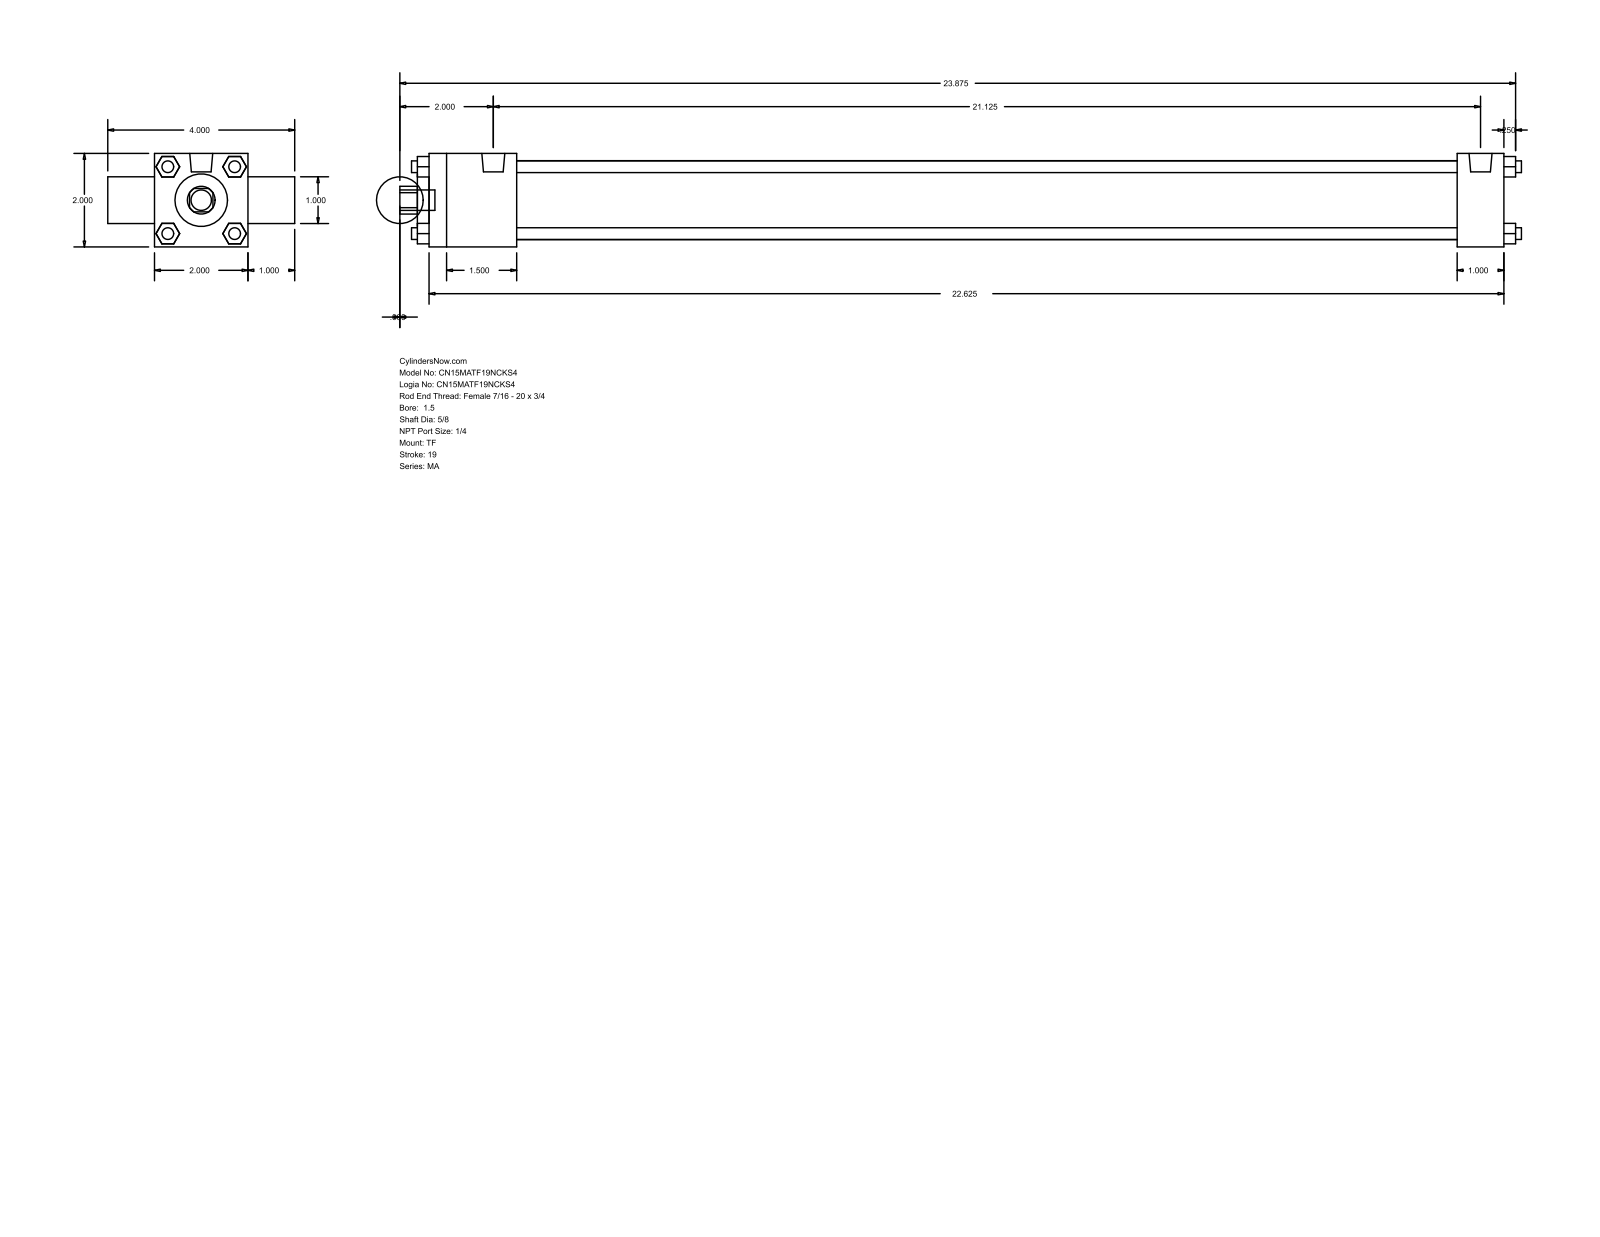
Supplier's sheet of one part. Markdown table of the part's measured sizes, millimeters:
| quantity | value |
| --- | --- |
| part name | MA_TF__0150_0.625 |
| STEP written by | GSSL Pune (CONFIG_CONTROL_DESIGN) |
| units | millimeters |
| bodies | 0 solids, 120 faces (92 planar, 28 cylindrical, 0 other) |
| overall size | 609.6 × 101.6 × 50.8 |
| round holes (diameter × count) | 15.88 × 1, 25.4 × 1, 28.57 × 1, 42.93 × 1 |
| round bosses / shafts (diameter × count) | 6.35 × 4, 7.94 × 3, 12.49 × 2, 11.11 × 1 |
| partial cylindrical surfaces (radius × count) | 7.54 × 1 |
| main face-to-face distances | 50.8, 584.2, 25.4, 76.2, 47.62, 558.79, 511.17, 536.58, 25.41, 590.55 |
